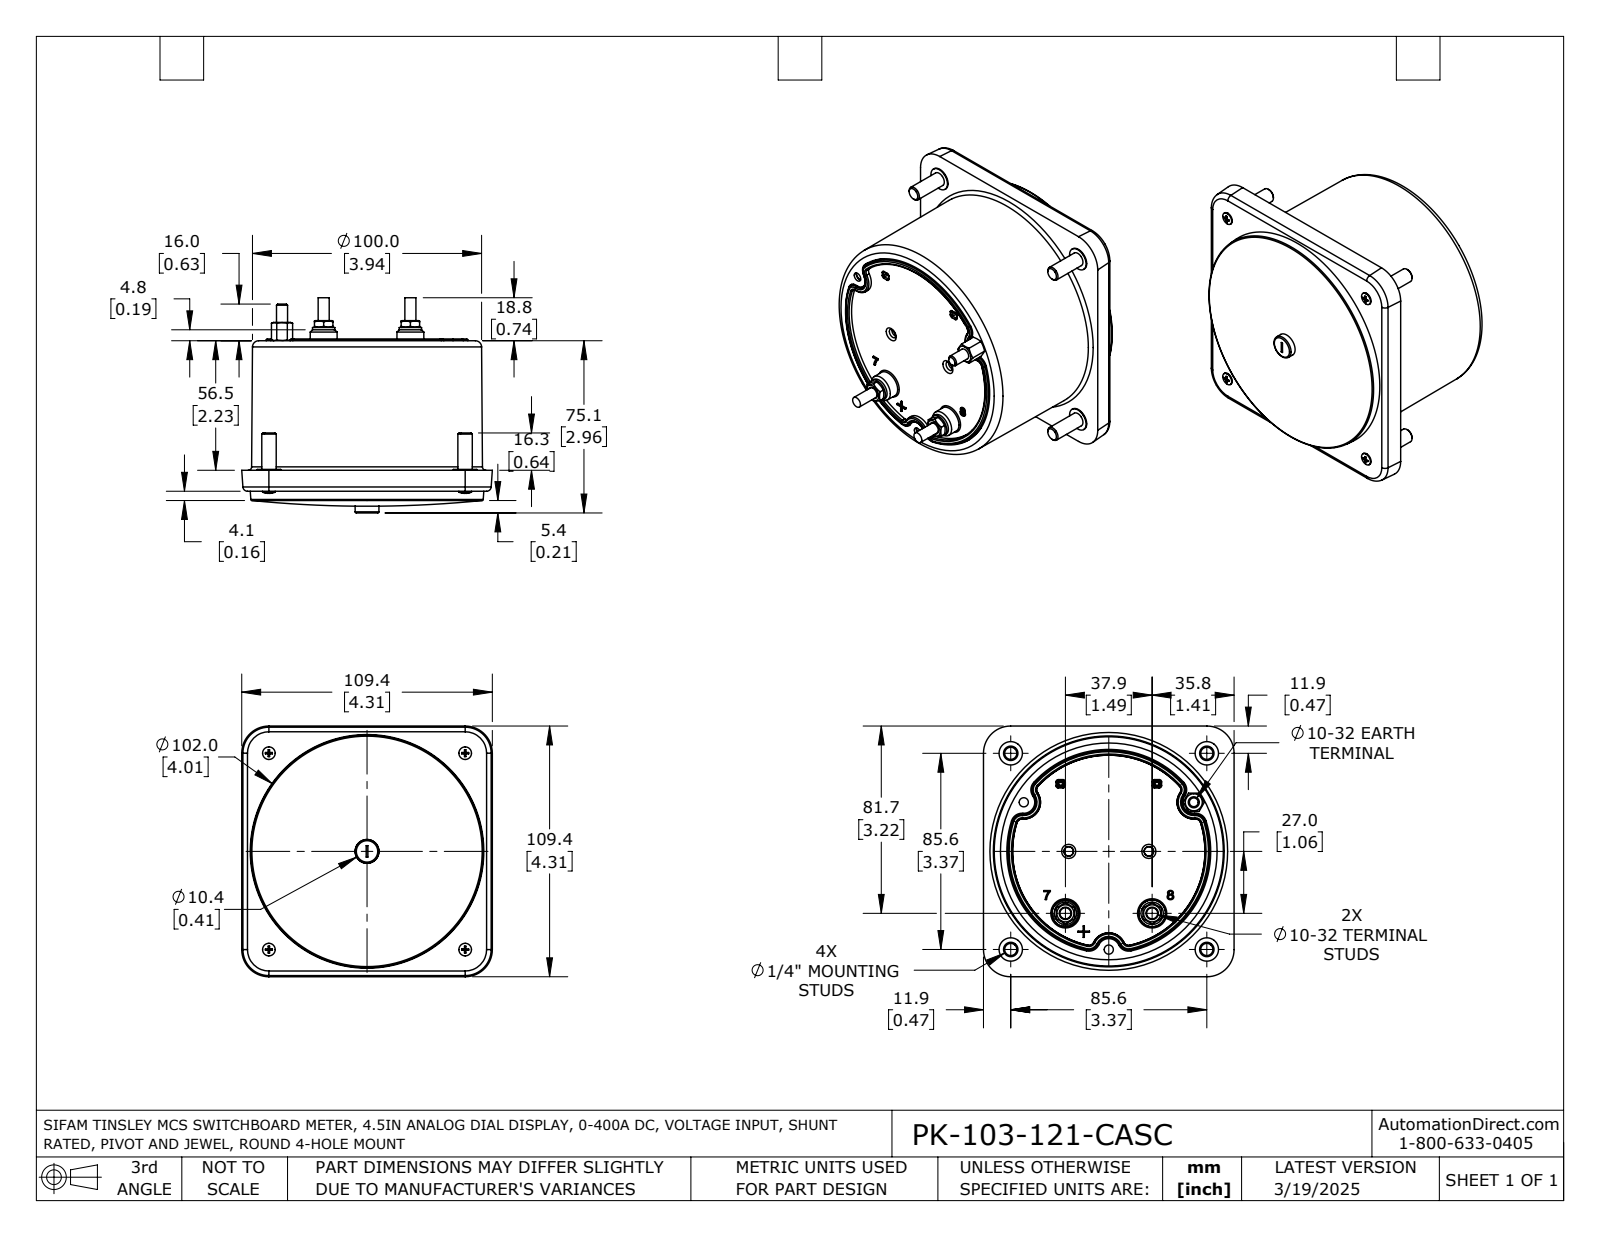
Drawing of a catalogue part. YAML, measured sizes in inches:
part_name: "PK-103-121-CASC"
step_written_by: "SolidWorks 2021 (AUTOMOTIVE_DESIGN)"
units: inches
bodies: {solids: 1, faces: 609, planar: 167, cylindrical: 141, other: 301}
overall_size: [4.307, 4.307, 3.697]
volume: 36.28
surface_area: 82.21
round_holes:
  - {diameter: 0.094, count: 4}
  - {diameter: 0.138, count: 4}
  - {diameter: 0.315, count: 4}
  - {diameter: 0.157, count: 3}
  - {diameter: 0.209, count: 2}
round_bosses_or_shafts:
  - {diameter: 0.402, count: 4}
  - {diameter: 0.248, count: 4}
  - {diameter: 0.217, count: 4}
  - {diameter: 0.114, count: 4}
  - {diameter: 0.19, count: 3}
  - {diameter: 0.384, count: 2}
  - {diameter: 0.146, count: 1}
partial_cylinders:
  - {radius: 0.02, count: 24}
  - {radius: 0.189, count: 9}
  - {radius: 0.079, count: 4}
  - {radius: 1.752, count: 1}
face_to_face_distances: [2.177, 2.537, 0.36, 0.048, 2.225, 2.585, 0.489, 2.715, 2.667, 0.129]
hole_center_spacings: [3.372, 3.37, 3.374, 3.378, 3.38, 4.769, 0.971, 1.126]
